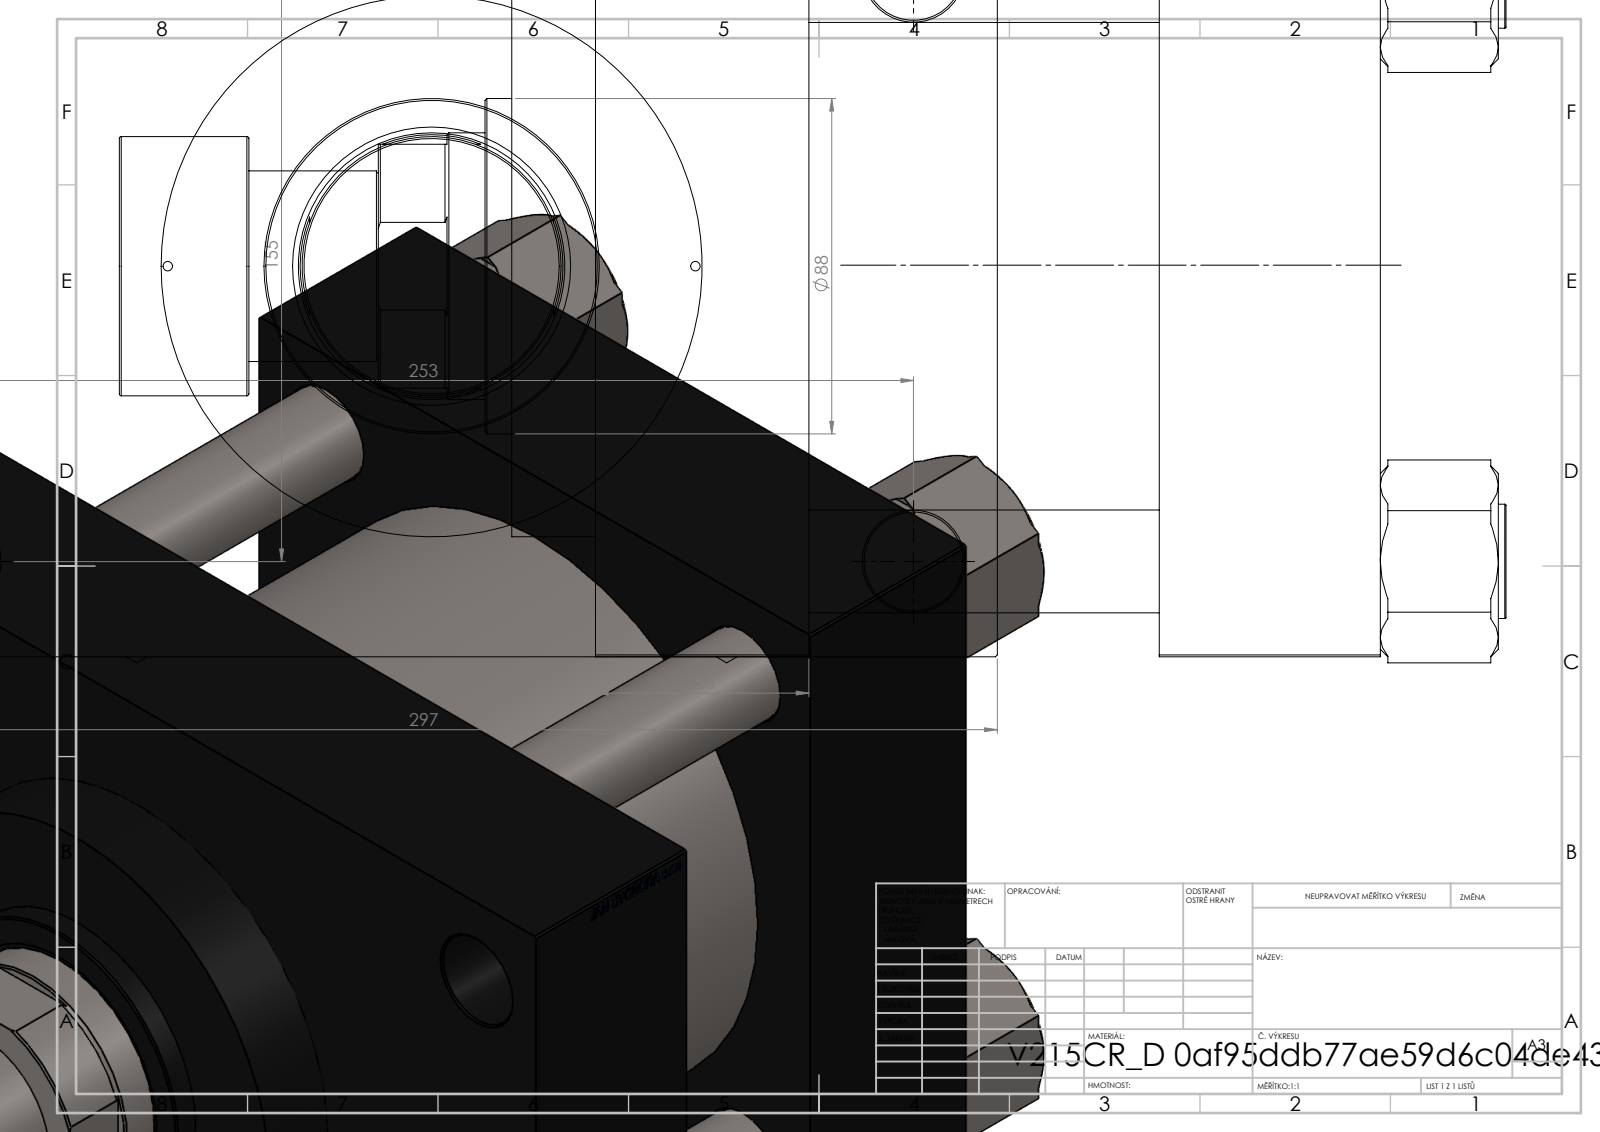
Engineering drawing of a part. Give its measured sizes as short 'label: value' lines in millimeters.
name: V215CR_ROD_END_F; V215_VC_A; V215CR_D_Body; V215CR_D_TYCINKA (+2 more)
written by: SolidWorks 2019 (CONFIG_CONTROL_DESIGN)
unit: mm
bodies: 12 solids, 1168 faces (550 planar, 96 cylindrical, 522 other)
size: 364 × 297 × 208.14
volume: 8 046 000 mm³; area: 749 616 mm²
holes: 4× ⌀26, 4× ⌀27, 2× ⌀2.5, 2× ⌀7, 2× ⌀33.24, 2× ⌀45, 1× ⌀46.5, 1× ⌀70, 1× ⌀73, 1× ⌀120, 1× ⌀142, 1× ⌀160
bosses: 4× ⌀30, 1× ⌀166, 1× ⌀88, 1× ⌀68, 1× ⌀50, 1× ⌀49
face distances: 58, 150, 92, 206, 148, 56, 205, 46, 251, 72
hole spacings: 49.05, 77.88, 96.35, 109.53, 148.35, 154.9, 162.53, 165.89
